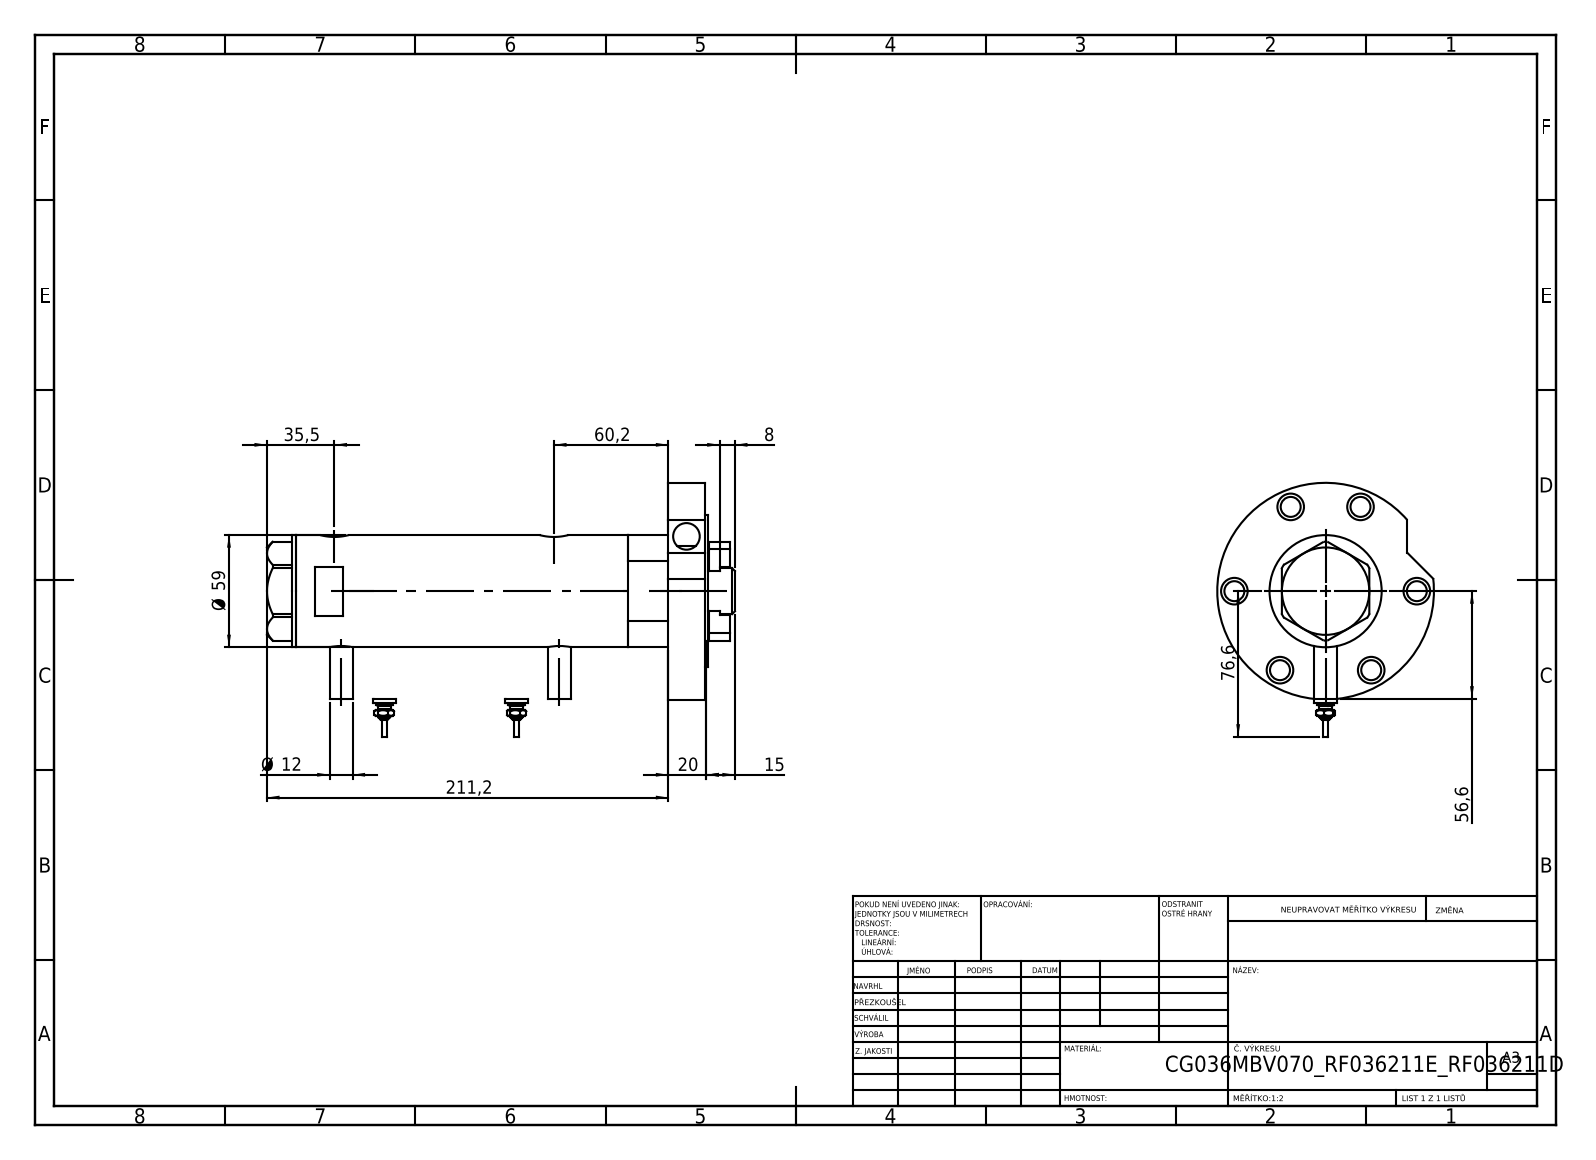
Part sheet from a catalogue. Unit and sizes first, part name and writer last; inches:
Units: inches
Overall size (bounding box): 9.693 × 5.26 × 4.488
Round holes (diameter × count): ⌀0.413 ×10, ⌀0.551 ×7, ⌀0.24 ×4, ⌀0.383 ×2, ⌀0.492 ×2, ⌀0.591 ×2, ⌀0.335 ×1, ⌀0.984 ×1, ⌀1.043 ×1, ⌀1.417 ×1, ⌀1.575 ×1, ⌀1.89 ×1
Round bosses / shafts (diameter × count): ⌀0.472 ×4, ⌀0.354 ×2, ⌀0.276 ×2, ⌀0.177 ×2, ⌀0.098 ×2, ⌀4.488 ×1, ⌀3.15 ×1, ⌀2.323 ×1
Main face-to-face distances: 0.079, 0.748, 0.827, 8.551, 7.724, 8.472, 5.402, 2.323, 3.071, 3.15
Hole centre spacings: 1.89, 0.784, 1.815, 2.254, 0.472, 1.111, 1.137, 1.385
Volume: 43.39 in³ · Surface area: 238.9 in²
Bodies: 9 solids, 296 faces (114 planar, 118 cylindrical, 64 other)
Part name (STEP PRODUCT): V270CG_RF211E; V270CG_VC; V270CG_RF211D; V270CG_MIDDLE (+3 more)
STEP written by: SolidWorks 2019 (CONFIG_CONTROL_DESIGN)
